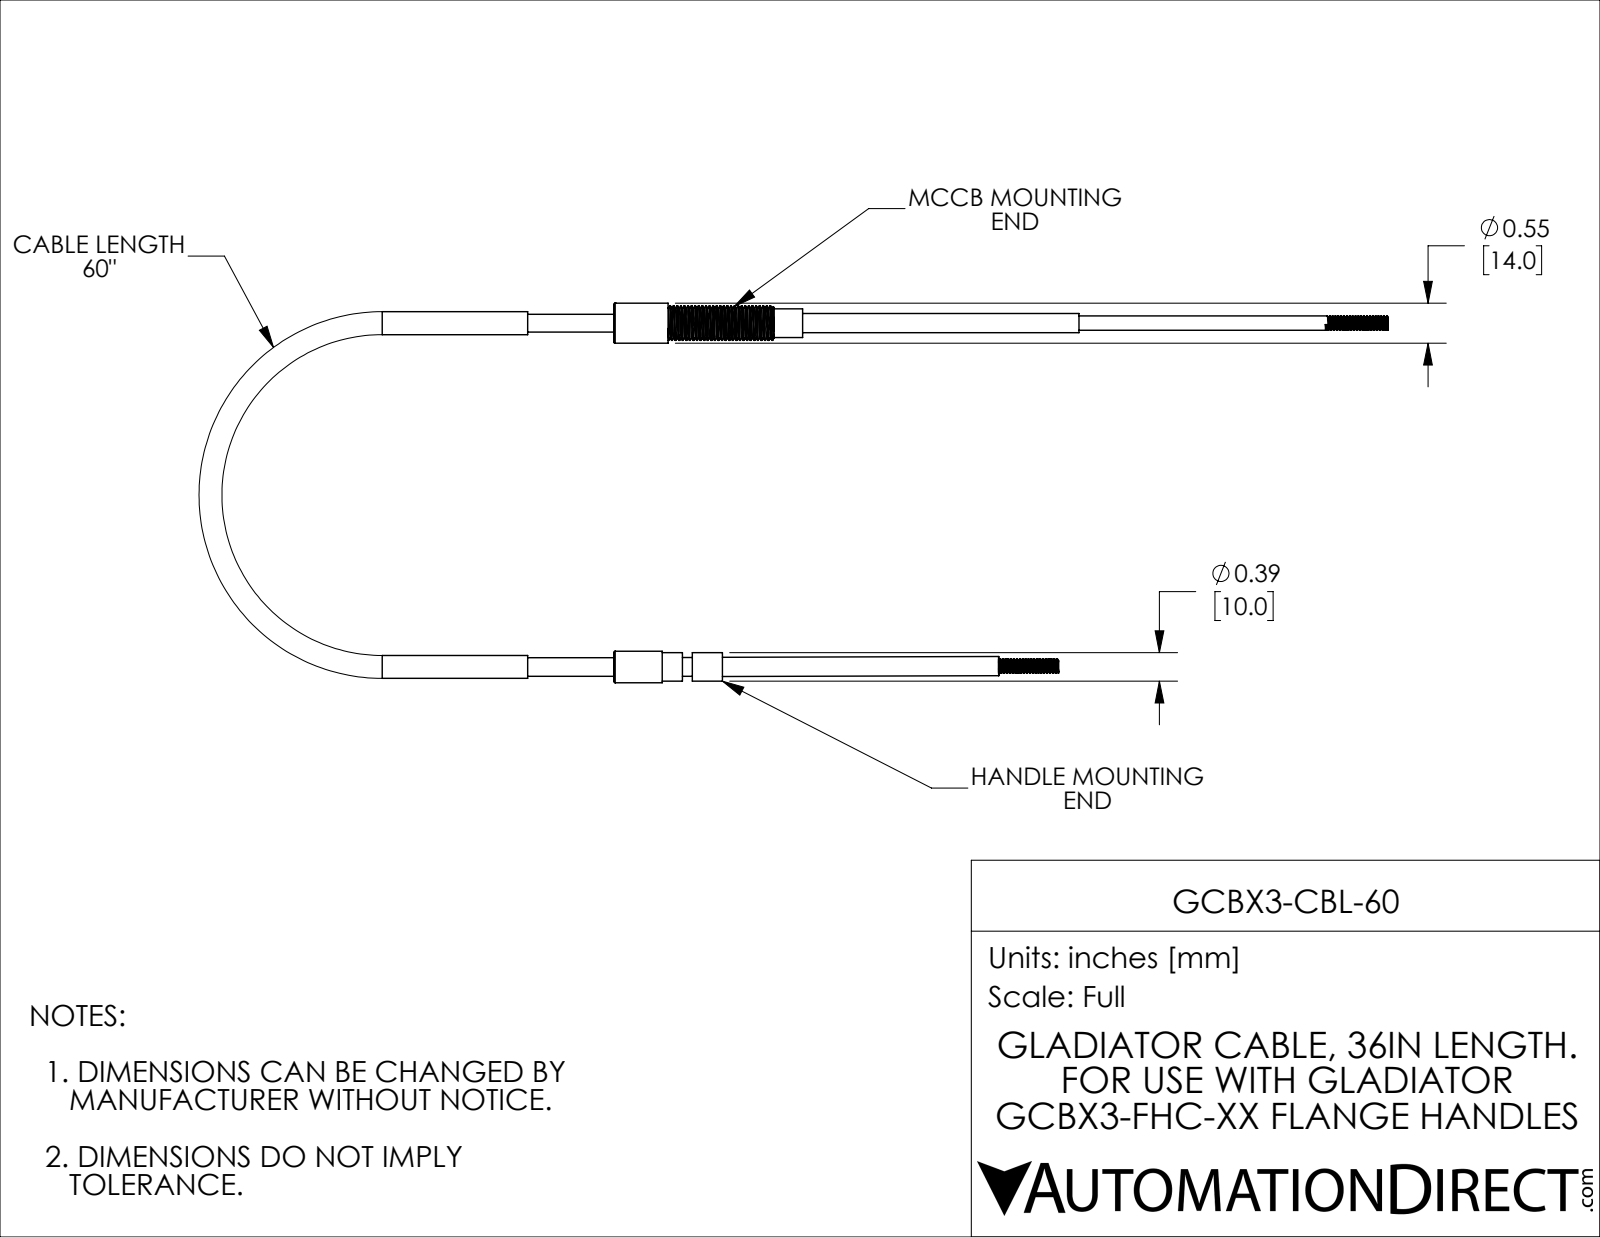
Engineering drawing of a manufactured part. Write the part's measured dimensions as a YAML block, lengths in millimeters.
part_name: "GCBX3-CBL-60_1; GCBX3-CBL-60; GCBX3-CBL-60_2"
step_written_by: "SolidWorks 2021 (CONFIG_CONTROL_DESIGN)"
units: millimeters
bodies: {solids: 9, faces: 262, planar: 29, cylindrical: 181, other: 52}
overall_size: [351.3, 132.5, 14]
volume: 24730
surface_area: 21400
round_holes:
  - {diameter: 5.1, count: 2}
  - {diameter: 3, count: 1}
  - {diameter: 8, count: 1}
round_bosses_or_shafts:
  - {diameter: 10, count: 2}
  - {diameter: 6.7, count: 2}
  - {diameter: 5, count: 2}
  - {diameter: 14, count: 1}
  - {diameter: 12, count: 1}
  - {diameter: 11, count: 1}
  - {diameter: 8, count: 1}
  - {diameter: 7.3, count: 1}
face_to_face_distances: [30, 80.8, 50.8, 66, 96, 146.8, 19, 47, 49, 10.5]
